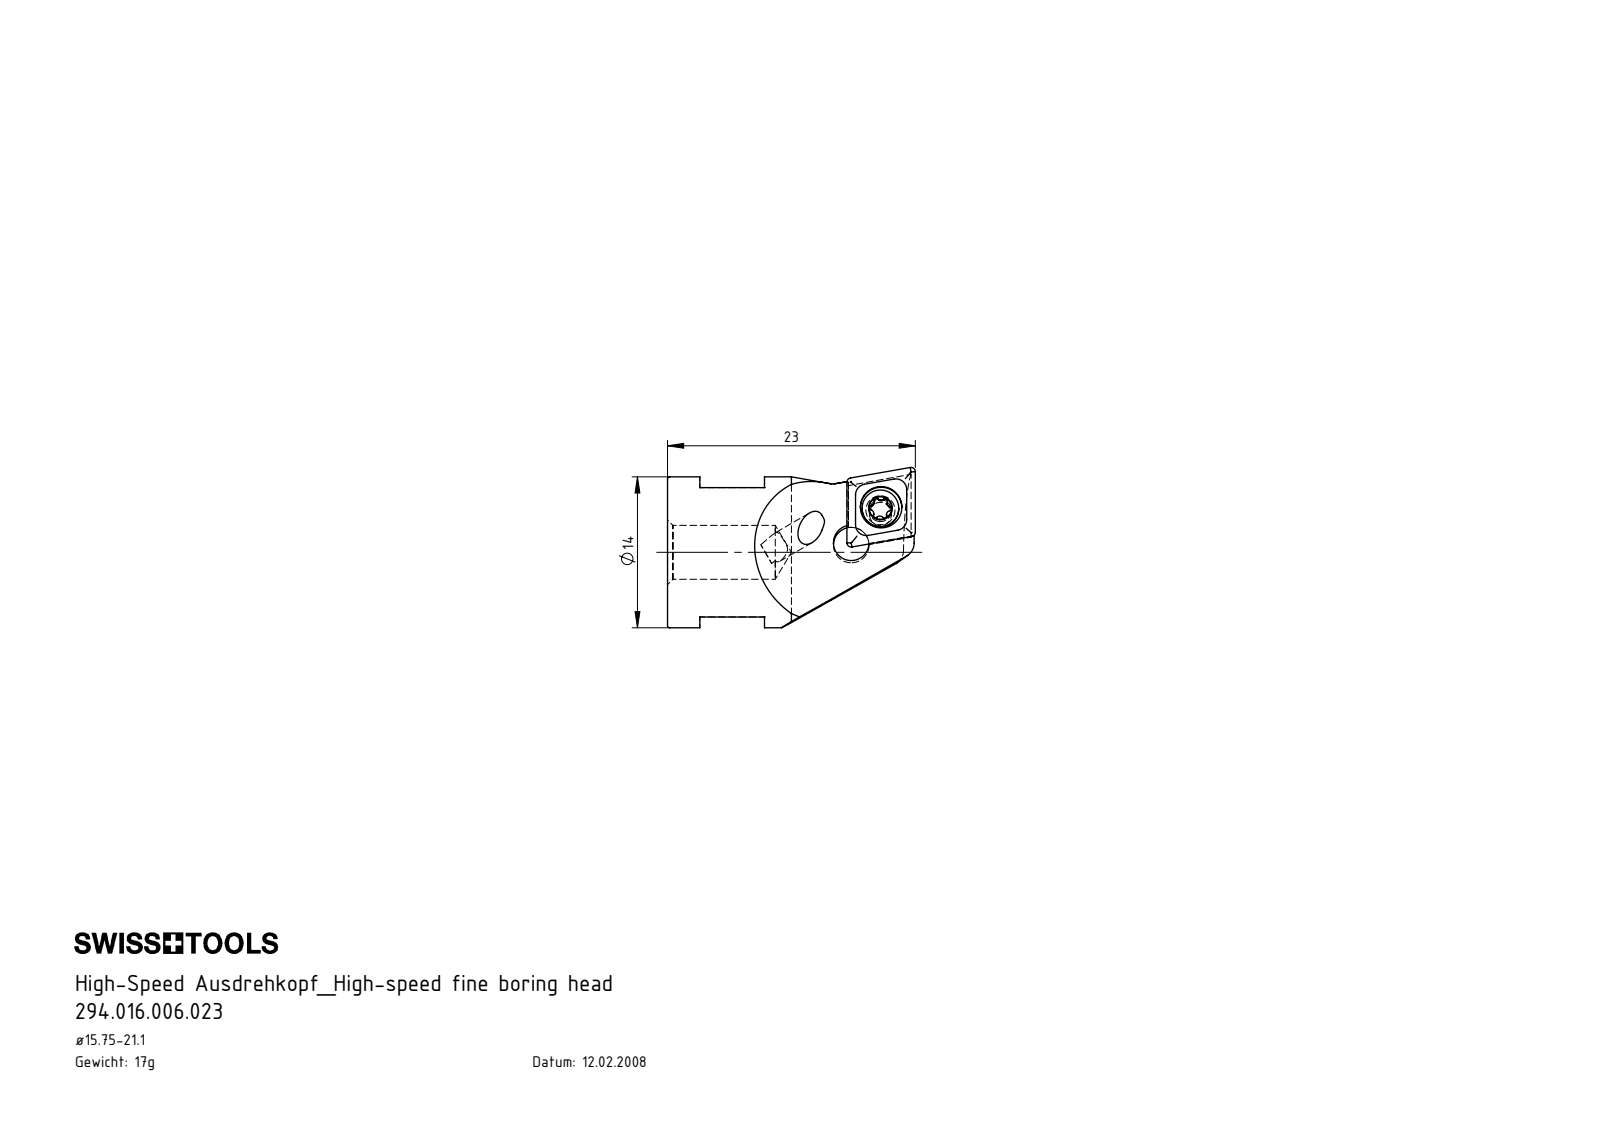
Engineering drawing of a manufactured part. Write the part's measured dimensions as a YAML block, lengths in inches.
part_name: "WCA-ER2.001.006_A; HS6.A16.K11.023; HS6-A16.K11.023_A; CCMT060204"
step_written_by: "SolidWorks 2017 (AUTOMOTIVE_DESIGN)"
units: inches
bodies: {solids: 3, faces: 125, planar: 34, cylindrical: 35, other: 56}
overall_size: [0.906, 0.586, 0.57]
volume: 0.132
surface_area: 2.344
round_holes:
  - {diameter: 0.081, count: 1}
  - {diameter: 0.098, count: 1}
  - {diameter: 0.11, count: 1}
  - {diameter: 0.13, count: 1}
  - {diameter: 0.152, count: 1}
  - {diameter: 0.197, count: 1}
round_bosses_or_shafts:
  - {diameter: 0.551, count: 1}
  - {diameter: 0.134, count: 1}
  - {diameter: 0.098, count: 1}
partial_cylinders:
  - {radius: 0.008, count: 6}
  - {radius: 0.014, count: 5}
  - {radius: 0.014, count: 1}
  - {radius: 0.02, count: 1}
  - {radius: 0.055, count: 1}
face_to_face_distances: [0.472, 0.09, 0.236, 0.094, 0.118, 0.354, 0.661, 0.543, 0.307, 0.058]
hole_center_spacings: [0.166, 0.17]
